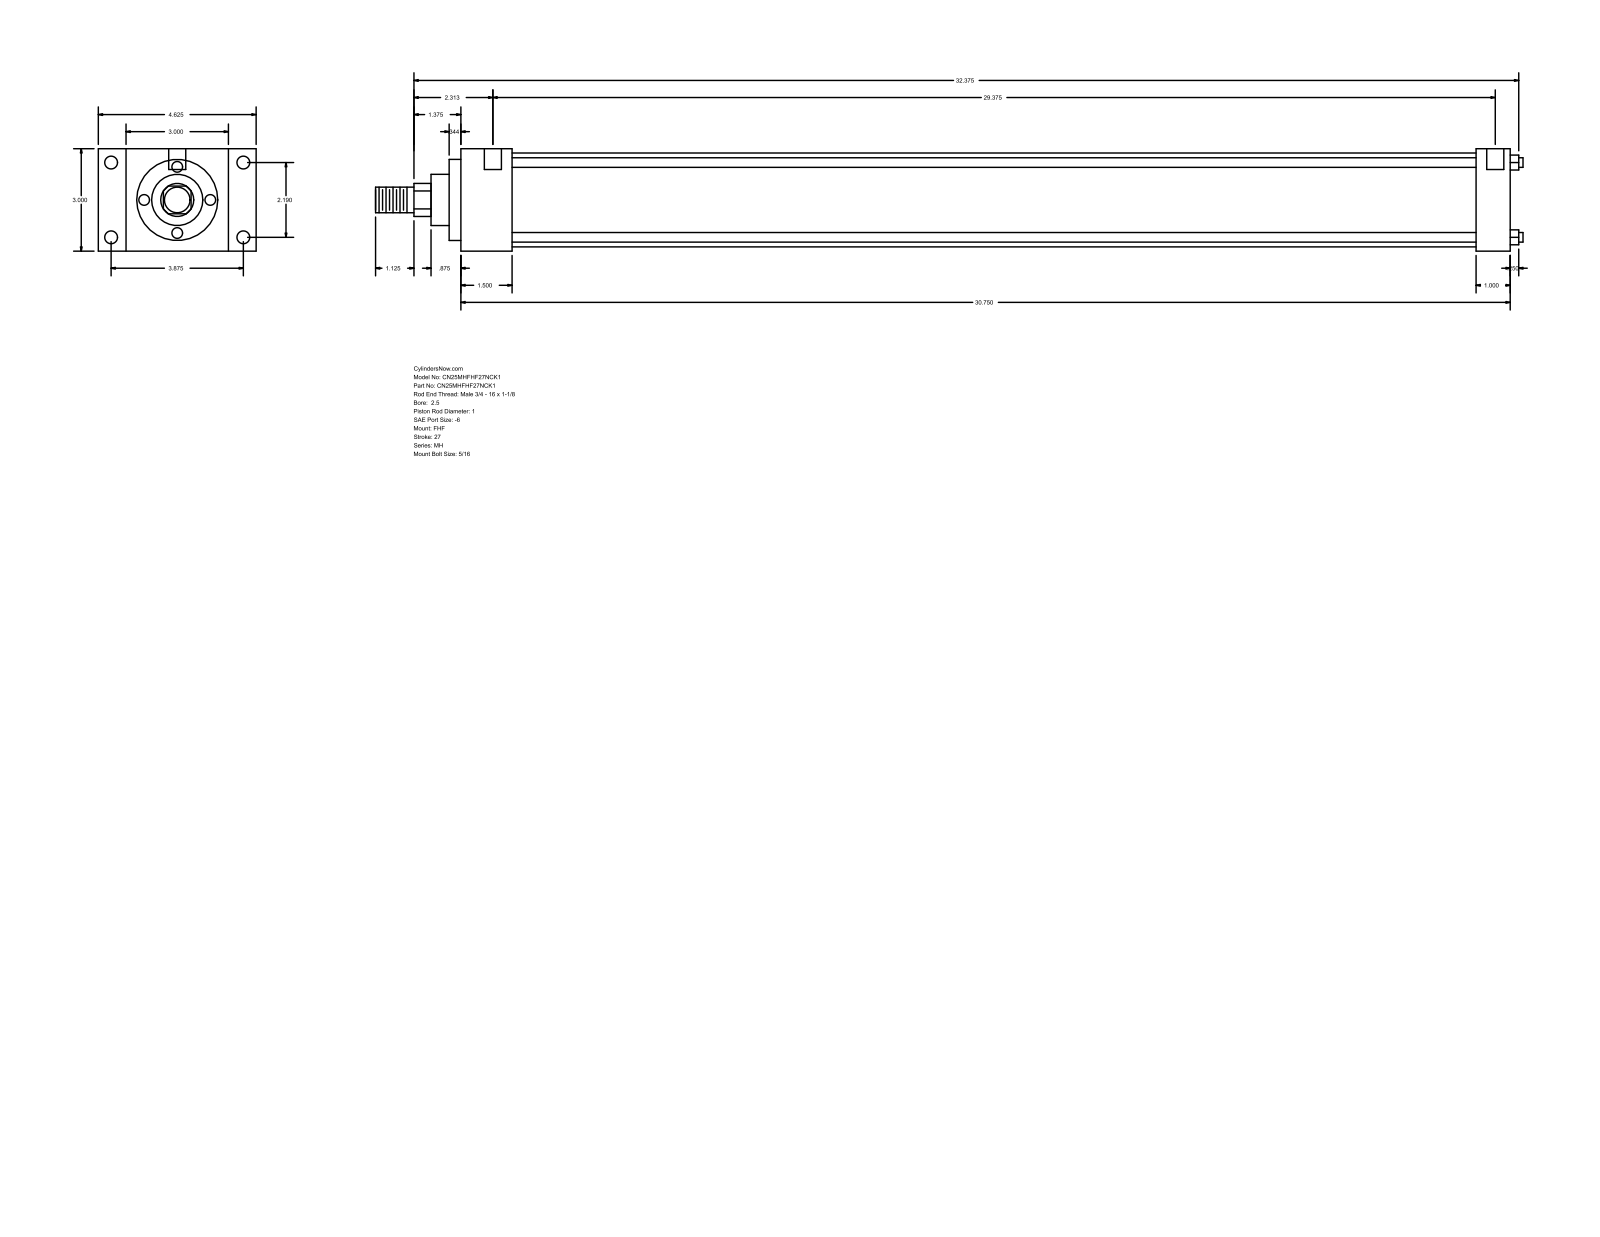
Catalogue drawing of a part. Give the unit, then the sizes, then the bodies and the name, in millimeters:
Units: millimetres
Overall size (bounding box): 854.08 × 117.47 × 76.2
Round holes (diameter × count): ⌀5.56 ×4, ⌀9.53 ×4, ⌀12.7 ×2
Round bosses / shafts (diameter × count): ⌀7.14 ×4, ⌀69.85 ×1, ⌀60.33 ×1, ⌀38.1 ×1, ⌀25.4 ×1, ⌀19.05 ×1
Partial cylindrical surfaces — rounded edges, fillets, slot ends (radius × count): R12.29 ×1
Main face-to-face distances: 76.2, 781.06, 38.11, 742.95, 20.64, 96.84, 117.48, 755.66, 717.55, 25.4
Hole centre spacings: 55.62, 98.42, 113.05, 754.06, 3.18, 4.76, 746.12, 749.3
Bodies: 0 solids, 90 faces (61 planar, 29 cylindrical, 0 other)
Part name (STEP PRODUCT): MH_FHF__0250_1
STEP written by: GSSL Pune (CONFIG_CONTROL_DESIGN)
